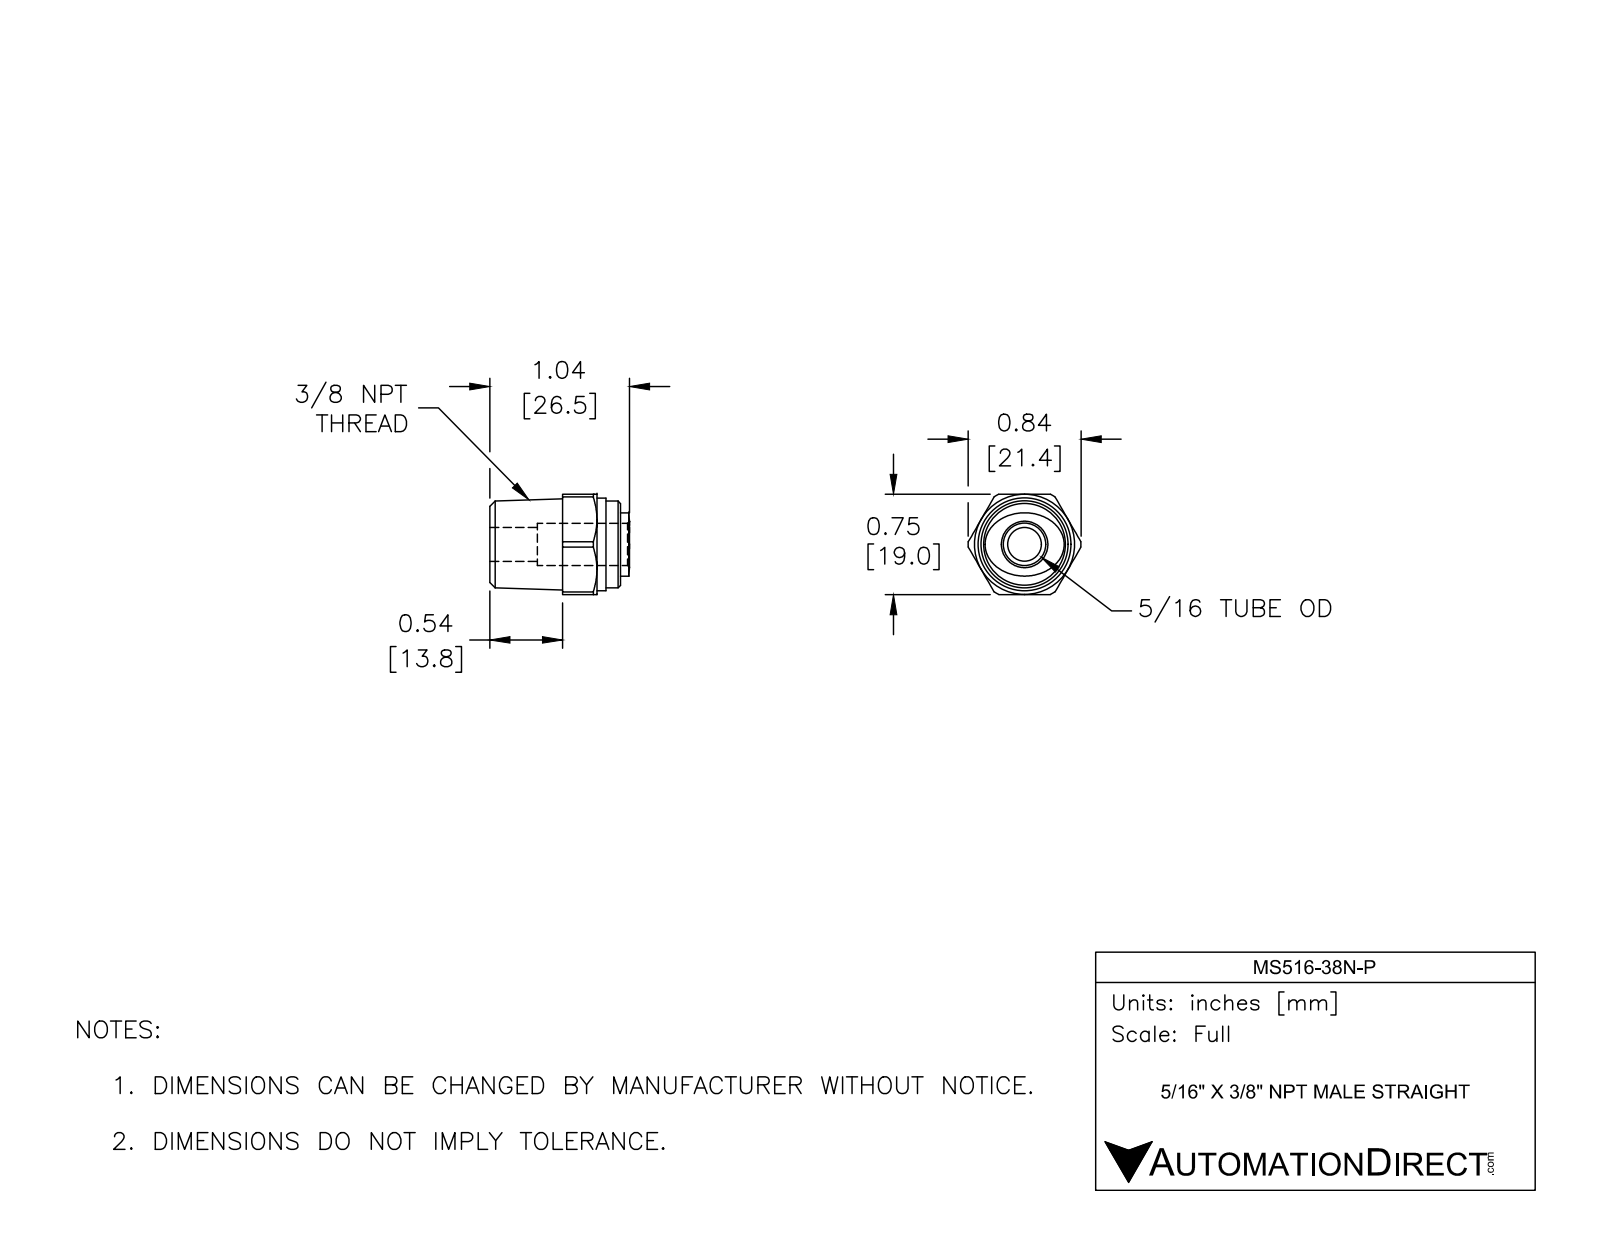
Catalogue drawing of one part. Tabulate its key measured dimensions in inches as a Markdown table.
| quantity | value |
| --- | --- |
| part name | MS516-38N-P |
| STEP written by | SolidWorks 2017 (AUTOMOTIVE_DESIGN) |
| units | inches |
| bodies | 1 solid, 46 faces (12 planar, 15 cylindrical, 19 other) |
| overall size | 1.043 × 0.843 × 0.748 |
| volume | 0.314 in³ |
| surface area | 3.955 in² |
| round holes (diameter × count) | 0.252 × 1, 0.315 × 1 |
| round bosses / shafts (diameter × count) | 0.693 × 1, 0.65 × 1 |
| partial cylindrical surfaces (radius × count) | 0.421 × 1 |
| main face-to-face distances | 0.748, 0.543, 0.976, 0.433, 0.799, 0.256, 0.177, 0.866, 0.323, 0.067 |
